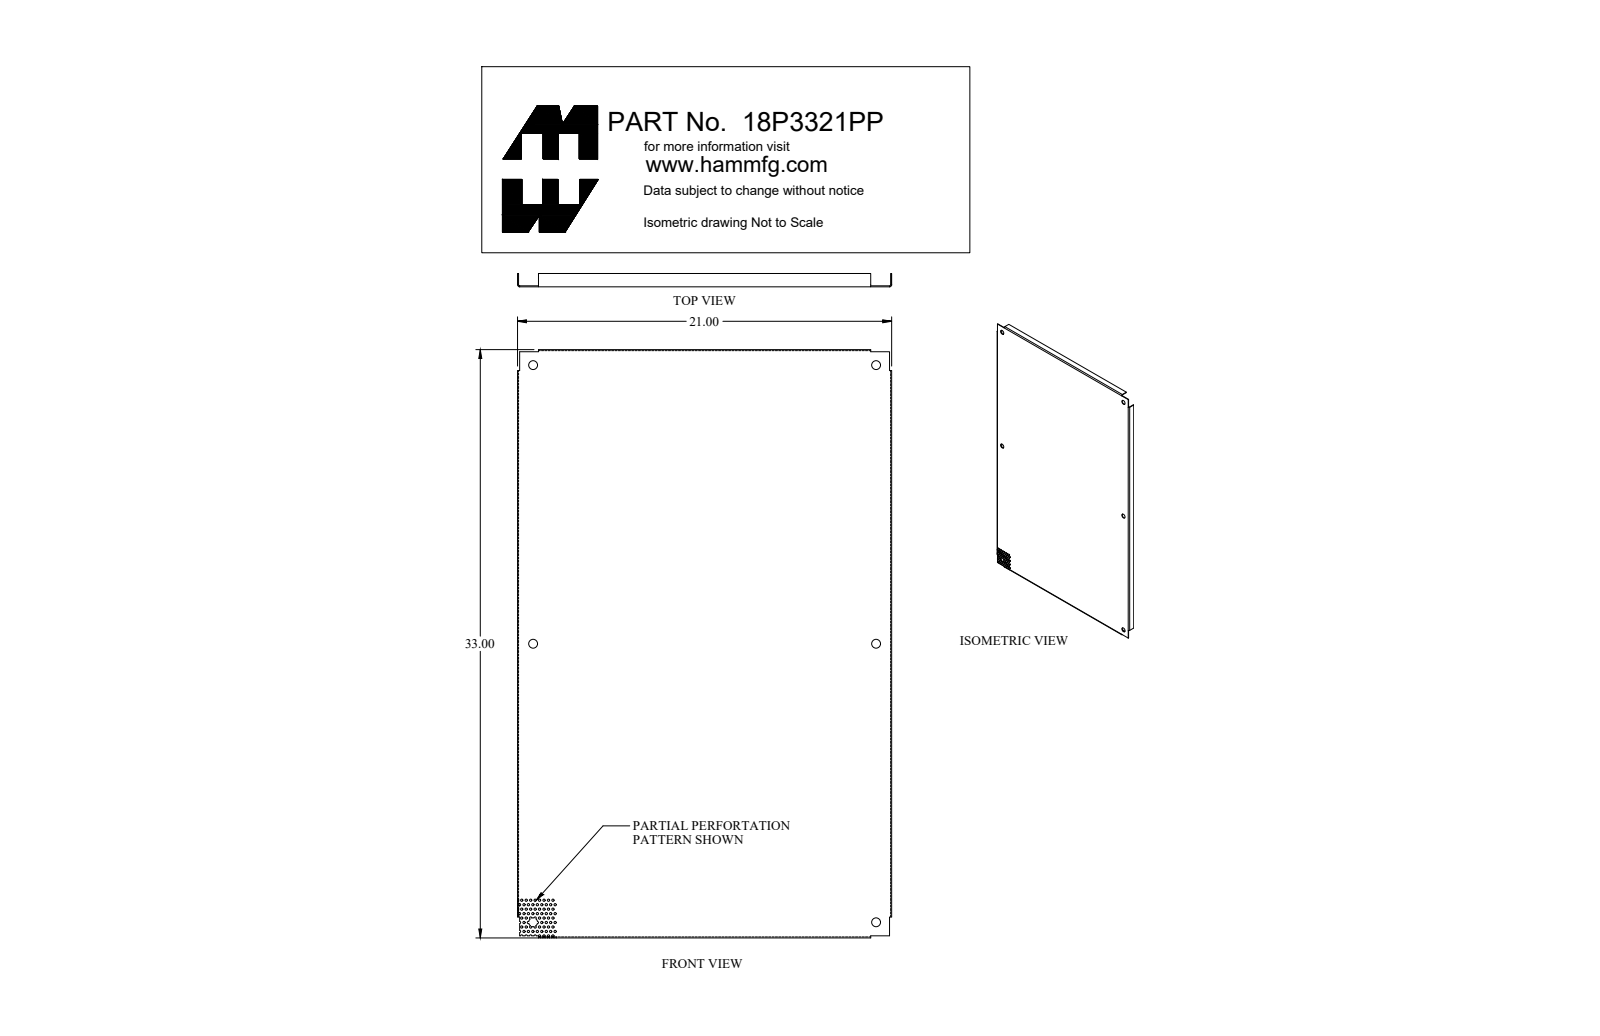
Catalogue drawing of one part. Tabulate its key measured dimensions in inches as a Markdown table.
| quantity | value |
| --- | --- |
| part name | 18P3321PP_Default |
| STEP written by | SolidWorks 2018 (CONFIG_CONTROL_DESIGN) |
| units | inches |
| bodies | 1 solid, 258 faces (43 planar, 207 cylindrical, 8 other) |
| overall size | 33 × 21 × 0.75 |
| volume | 43.08 in³ |
| surface area | 1 520 in² |
| round holes (diameter × count) | 0.125 × 74, 0.5 × 5 |
| partial cylindrical surfaces (radius × count) | 0.063 × 17, 0.062 × 8, 0.029 × 4, 0.086 × 4, 0.25 × 1 |
| main face-to-face distances | 0.057, 20.943, 32.943, 20.886, 21, 32.886, 33, 0.75, 0.693, 0.102 |
| hole center spacings | 0.28, 0.5, 0.25, 0.559, 0.451, 0.673, 0.707, 0.75 |
